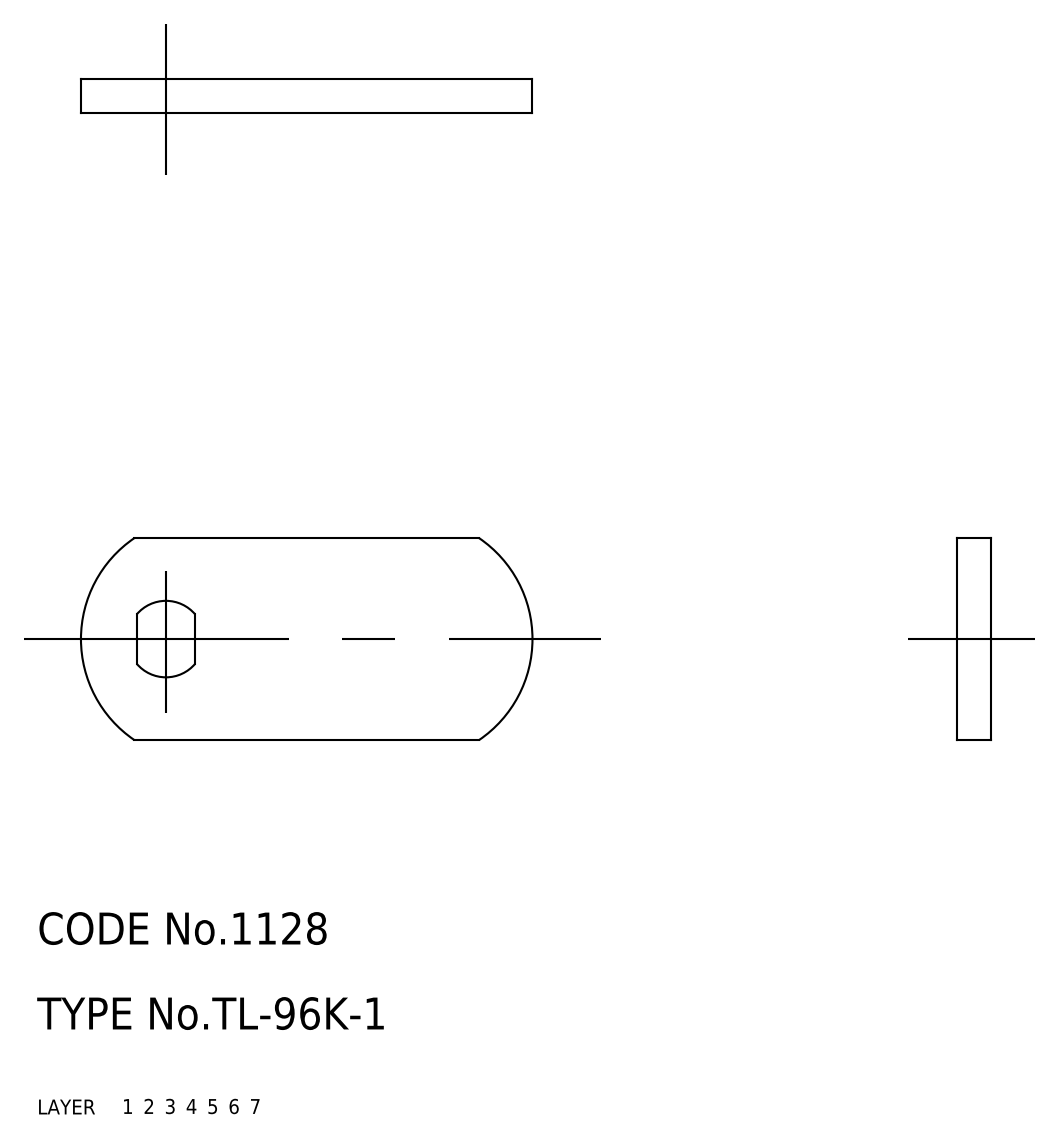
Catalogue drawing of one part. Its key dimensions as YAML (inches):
part_name: "cam"
step_written_by: "CADfix (AUTOMOTIVE_DESIGN)"
units: inches
bodies: {solids: 1, faces: 10, planar: 0, cylindrical: 0, other: 10}
overall_size: [1.673, 0.748, 0.126]
volume: 0.14
surface_area: 2.871
